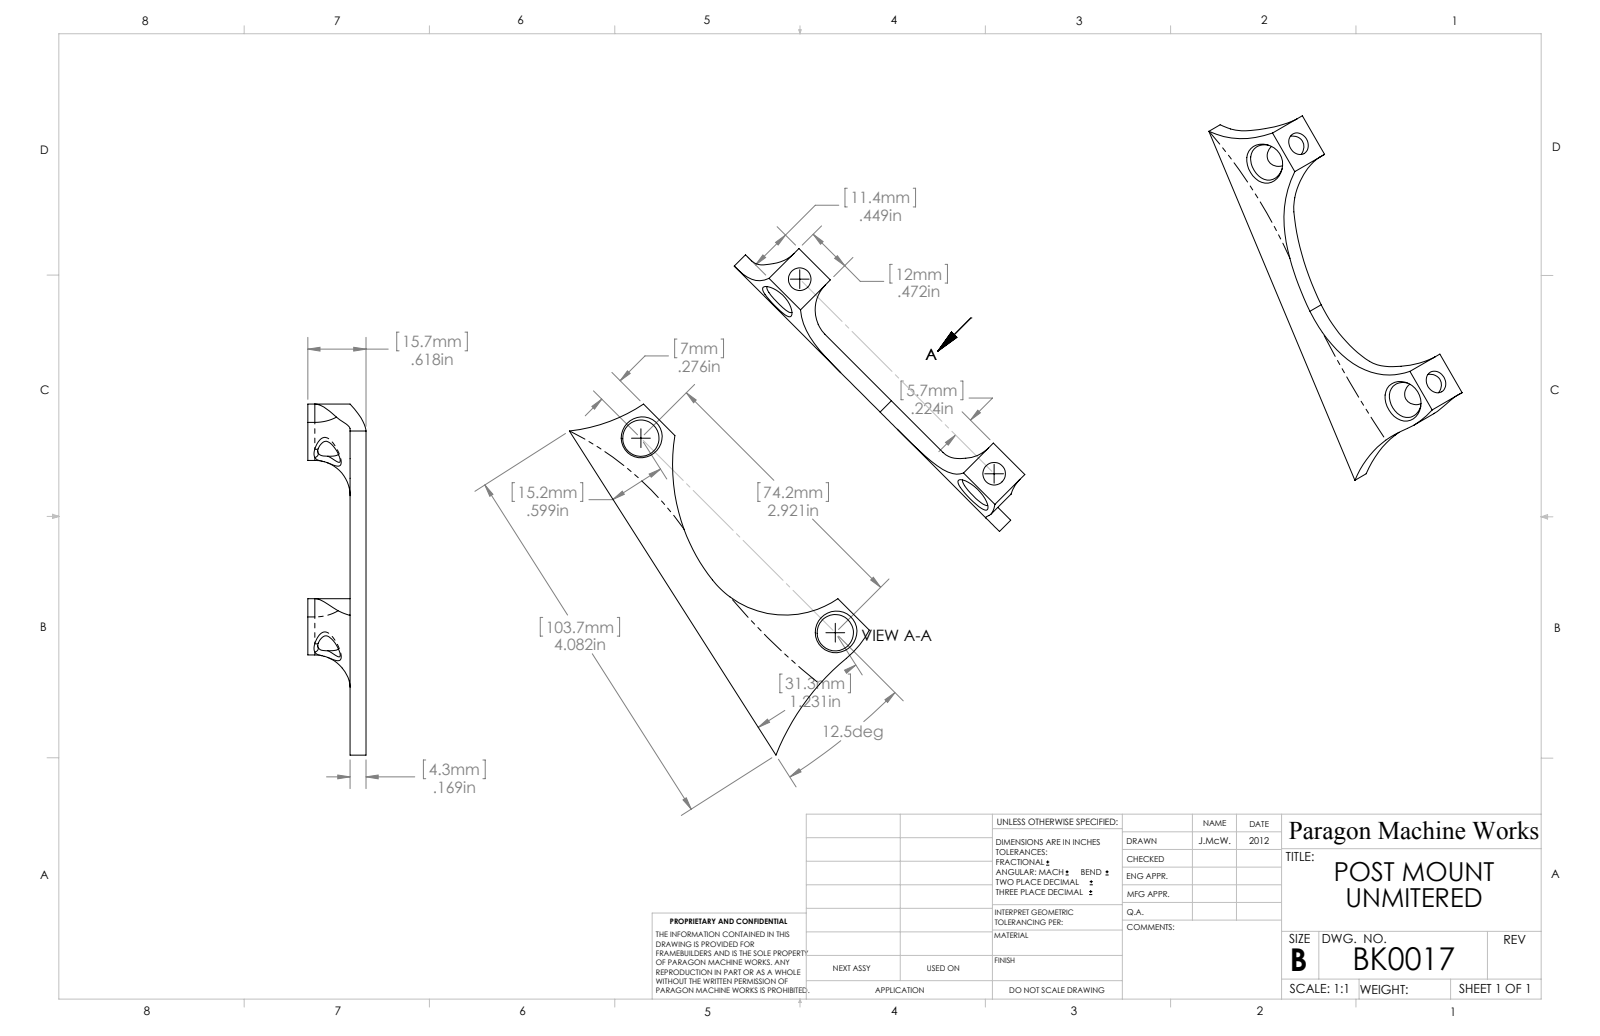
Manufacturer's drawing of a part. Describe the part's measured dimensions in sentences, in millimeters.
The part is named "BK0017". Its 3-D file was written by "SolidWorks 2012 (AUTOMOTIVE_DESIGN)". It is 1 solid with 43 faces: 12 planar, 19 cylindrical and 12 other. Overall it measures 94.68 by 80.93 by 15.7 millimeters. Its volume is 9 251 cubic millimeters and its surface area 6 099 square millimeters. Round holes: 2 of diameter 6.1, 2 of diameter 9.8. Partial cylindrical surfaces (rounded edges, fillets, slot ends): 4 of radius 9.53, 2 of radius 6, 2 of radius 25, 1 of radius 45, 1 of radius 50, 1 of radius 65. The main face-to-face distances are 4.3, 15.7, 11.4, 12, 74.19, 62.19, 86.19. The hole center spacings are 74.2.
